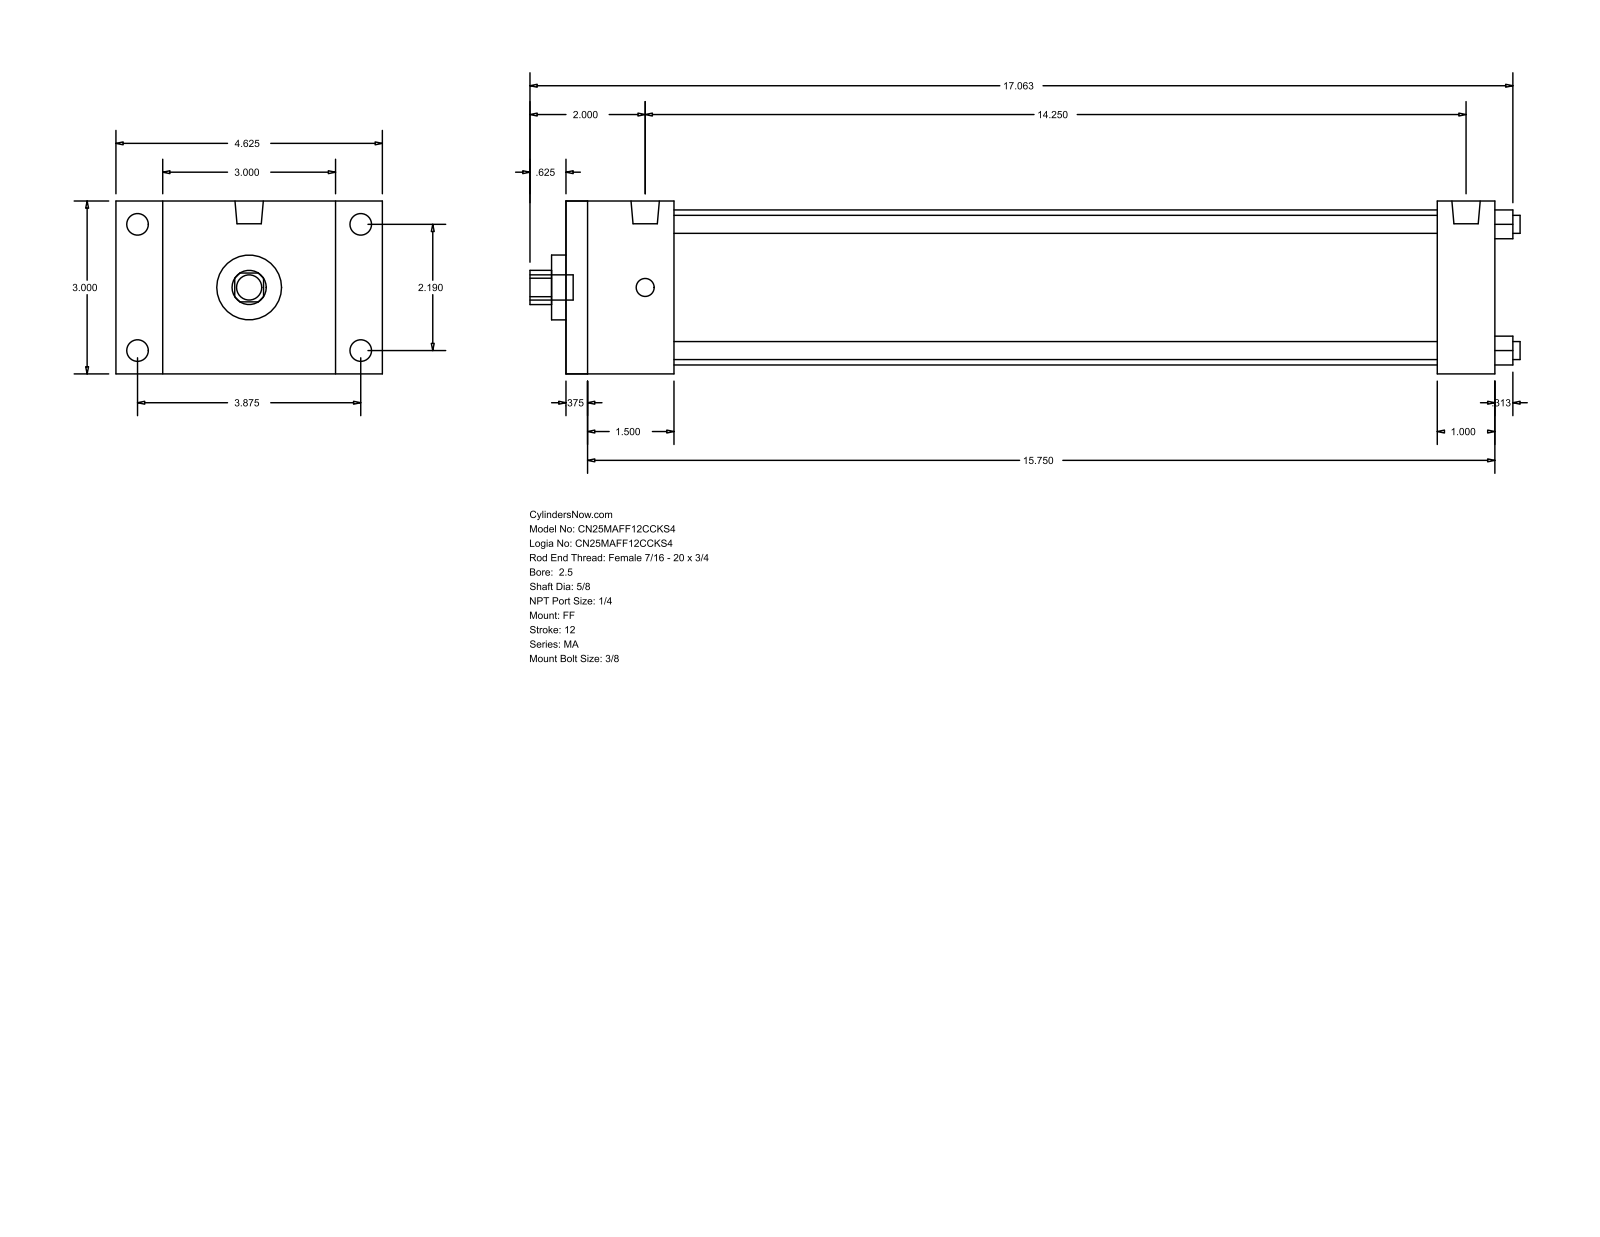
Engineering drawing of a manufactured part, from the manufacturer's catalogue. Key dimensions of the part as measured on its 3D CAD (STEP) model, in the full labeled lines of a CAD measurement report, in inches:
Part name (STEP PRODUCT): MA_FF__0250_0.625
STEP written by: GSSL Pune (CONFIG_CONTROL_DESIGN)
Units: inches
Bodies: 0 solids, 92 faces (64 planar, 28 cylindrical, 0 other)
Overall size (bounding box): 17.187 × 4.625 × 3
Round holes (diameter × count): ⌀0.313 ×4, ⌀0.625 ×1, ⌀1.125 ×1, ⌀2.69 ×1
Round bosses / shafts (diameter × count): ⌀0.375 ×4, ⌀0.313 ×4, ⌀0.492 ×2, ⌀0.437 ×1
Partial cylindrical surfaces — rounded edges, fillets, slot ends (radius × count): R0.297 ×1
Main face-to-face distances: 3, 16.125, 0.375, 15.75, 1, 1.875, 15.125, 1.5, 14.75, 13.25
Hole centre spacings: 1.548, 2.19, 3.097
